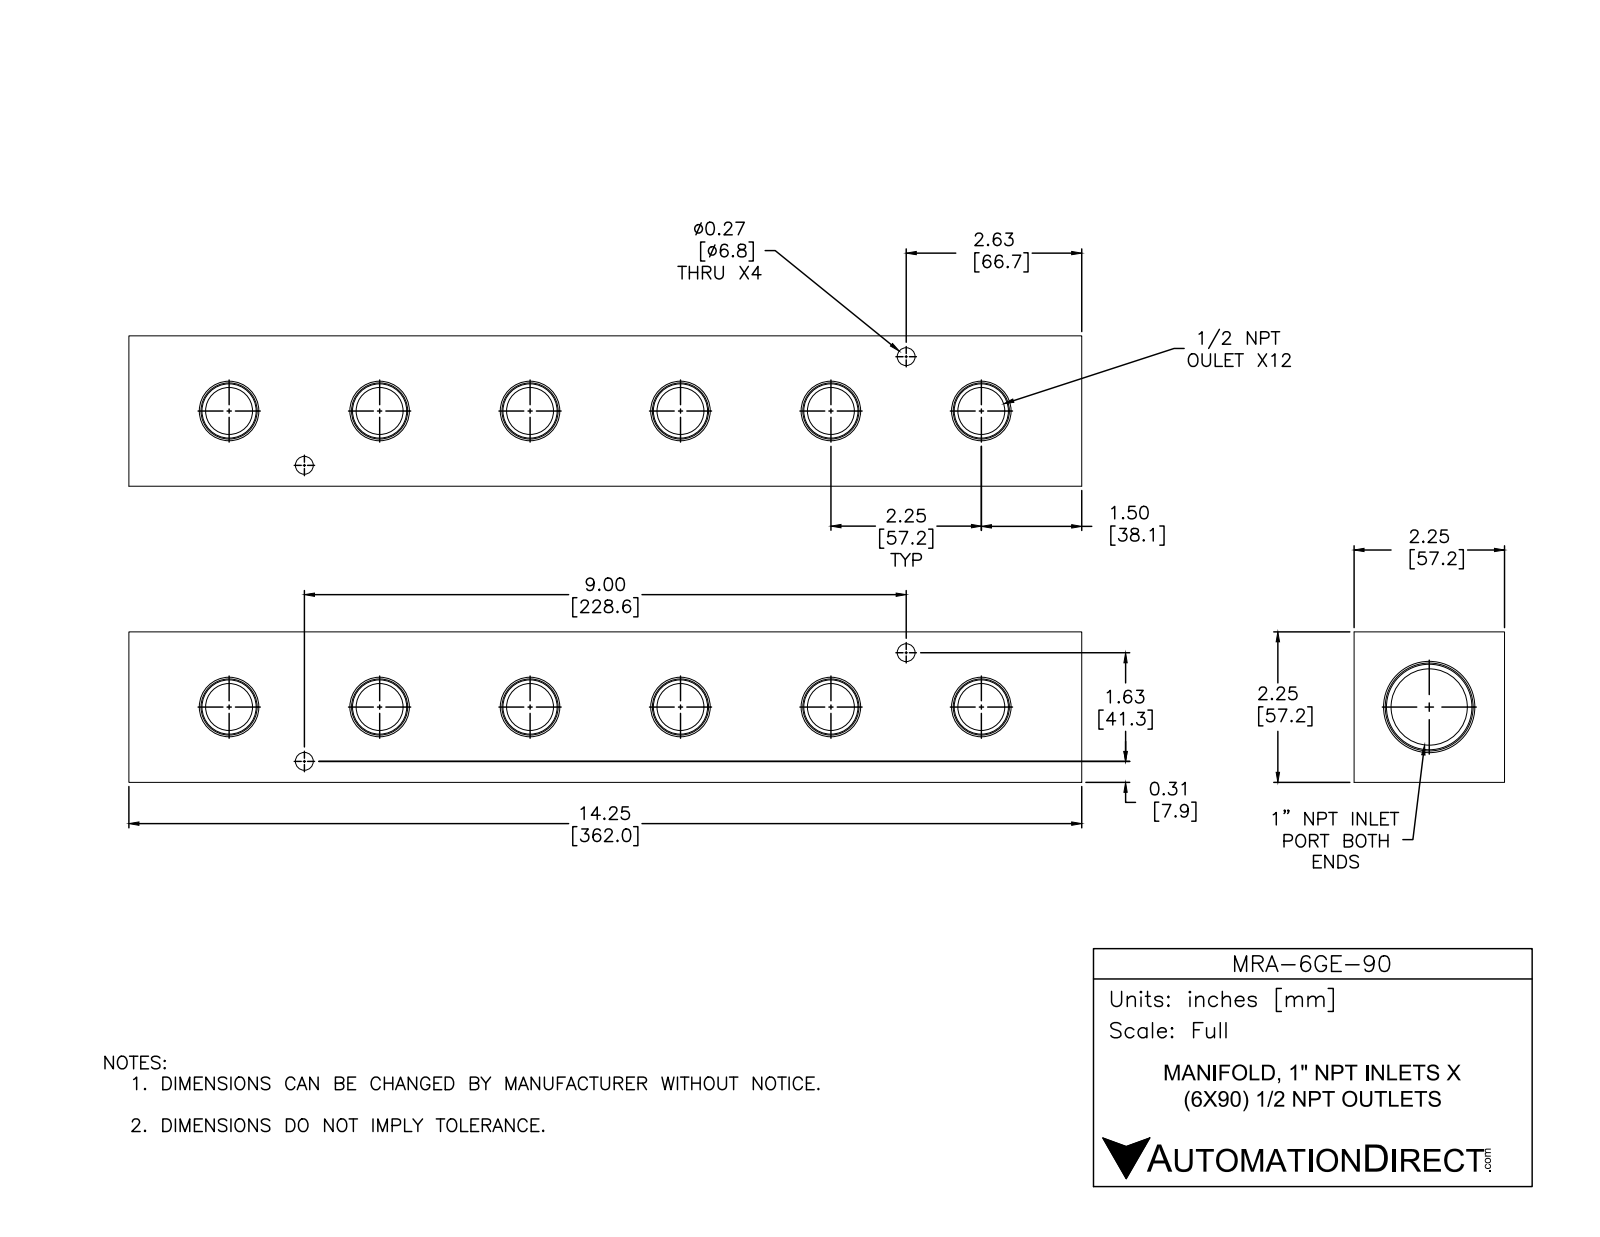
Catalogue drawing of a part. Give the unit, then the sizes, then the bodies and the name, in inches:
Units: inches
Overall size (bounding box): 14.25 × 2.25 × 2.25
Round holes (diameter × count): ⌀0.703 ×12, ⌀0.266 ×4, ⌀1.141 ×1
Main face-to-face distances: 2.25, 14.25, 0.53, 1.72, 0.66, 13.59, 12.93
Hole centre spacings: 1.388, 2.25, 2.25, 4.5, 7.917, 9, 10.158, 2.25
Volume: 53.04 in³ · Surface area: 202.5 in²
Bodies: 1 solid, 118 faces (20 planar, 42 cylindrical, 56 other)
Part name (STEP PRODUCT): MRA-6GE-90
STEP written by: SolidWorks 2015 (CONFIG_CONTROL_DESIGN)
